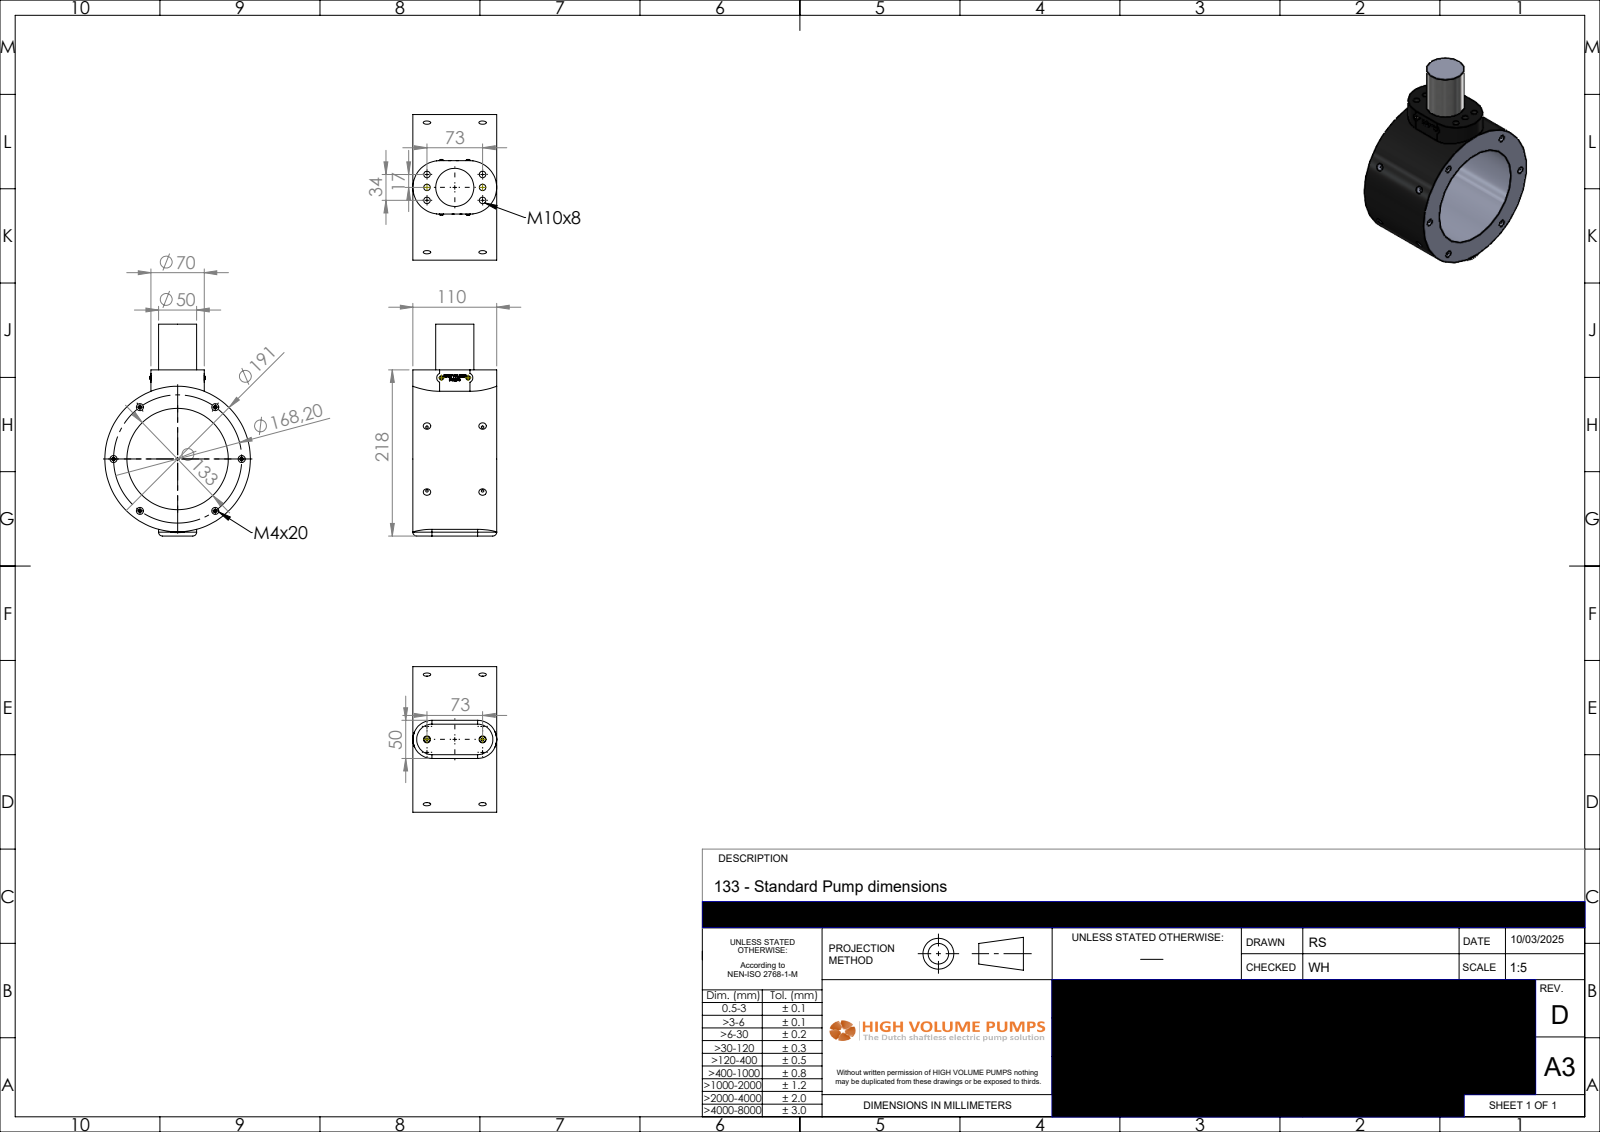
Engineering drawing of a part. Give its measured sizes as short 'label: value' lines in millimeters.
name: P-133-030-rev-D-SP
written by: SolidWorks 2024 (AUTOMOTIVE_DESIGN)
unit: mm
bodies: 1 solid, 606 faces (361 planar, 57 cylindrical, 188 other)
size: 278 × 191 × 110.06
volume: 1 918 000 mm³; area: 166 465 mm²
holes: 10× ⌀3.3, 6× ⌀4.5, 6× ⌀8.5, 1× ⌀133
bosses: 2× ⌀7.64, 2× ⌀5.7, 1× ⌀191, 1× ⌀50
rounds: 2× R5, 2× R6.25, 2× R25, 2× R35
face distances: 110.06, 218, 60, 278, 70, 10, 205.56, 12.44, 72.44, 50
hole spacings: 84.1, 73, 17, 74.95, 76.36, 149.87, 168.2, 34
